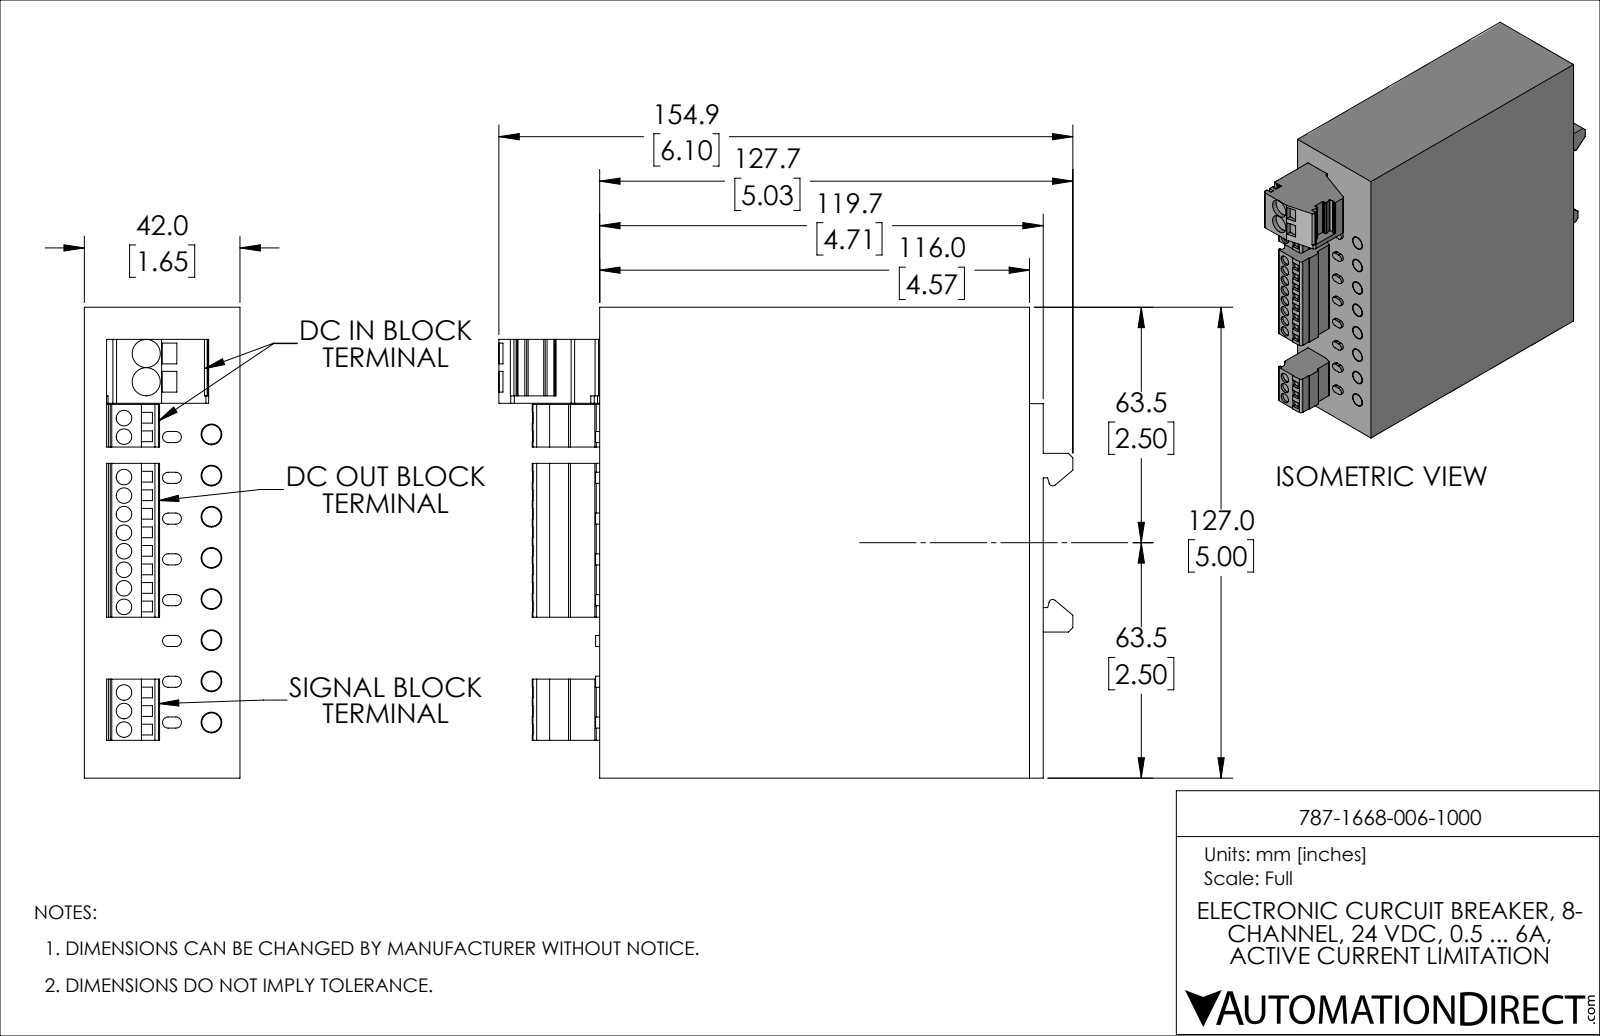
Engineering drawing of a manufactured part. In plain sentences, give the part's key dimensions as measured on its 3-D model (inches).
The part is named "787-1668/006-1000". Its 3-D file was written by "PARTsolutions (CONFIG_CONTROL_DESIGN)". It is 1 solid with 366 faces: 281 planar, 85 cylindrical and 0 other. Overall it measures 6.098 by 5 by 1.654 inches. Its volume is 40.26 cubic inches and its surface area 93.23 square inches. Round holes: 13 of diameter 0.165, 8 of diameter 0.22, 2 of diameter 0.299. Round bosses or shafts: 8 of diameter 0.205. Partial cylindrical surfaces (rounded edges, fillets, slot ends): 16 of radius 0.059, 12 of radius 0.008, 9 of radius 0.039, 4 of radius 0.016, 2 of radius 0.012, 2 of radius 0.019. The main face-to-face distances are 1.654, 5, 4.713, 0.146, 4.567, 0.236, 1.417, 0.199, 1.455, 1.02. The hole center spacings are 0.197, 0.394, 0.437, 0.874, 0.591, 1.311, 0.787, 1.748.
